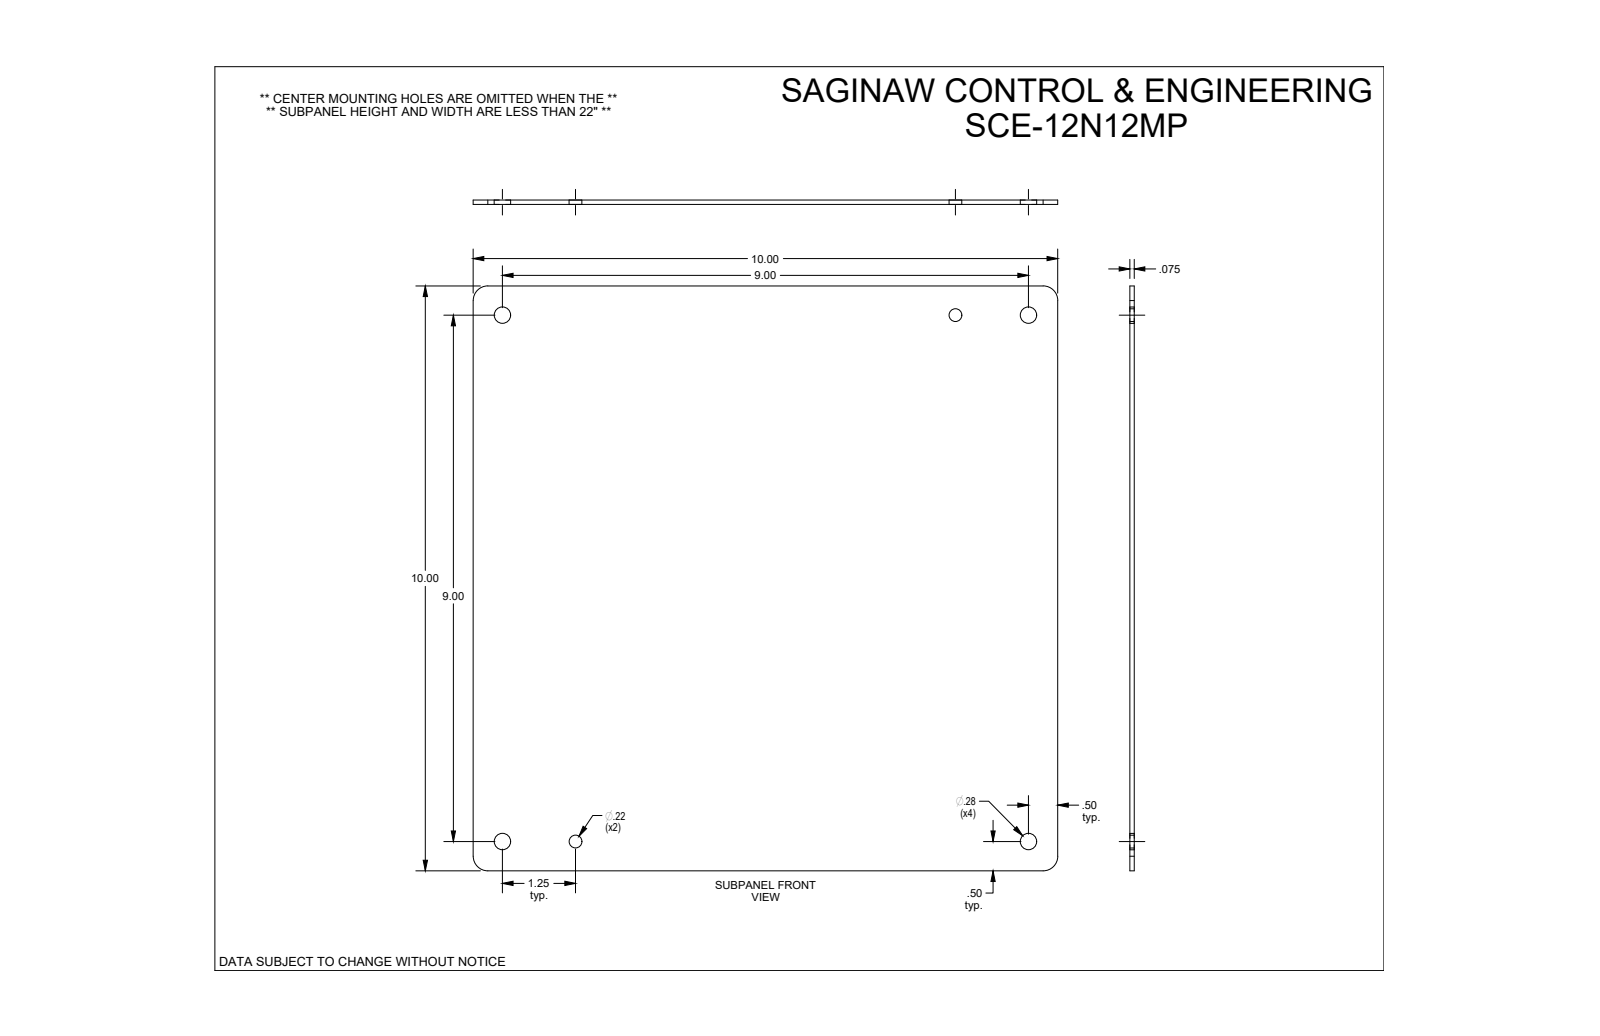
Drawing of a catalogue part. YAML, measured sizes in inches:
part_name: "SCE-12N12MP"
step_written_by: "SolidWorks 2019 (CONFIG_CONTROL_DESIGN)"
units: inches
bodies: {solids: 1, faces: 16, planar: 6, cylindrical: 10, other: 0}
overall_size: [10, 10, 0.075]
volume: 7.472
surface_area: 202.6
round_holes:
  - {diameter: 0.281, count: 4}
  - {diameter: 0.218, count: 2}
partial_cylinders:
  - {radius: 0.25, count: 4}
face_to_face_distances: [0.075, 10]
hole_center_spacings: [9, 1.25, 7.75, 9.086, 11.877, 12.728, 11.102]
